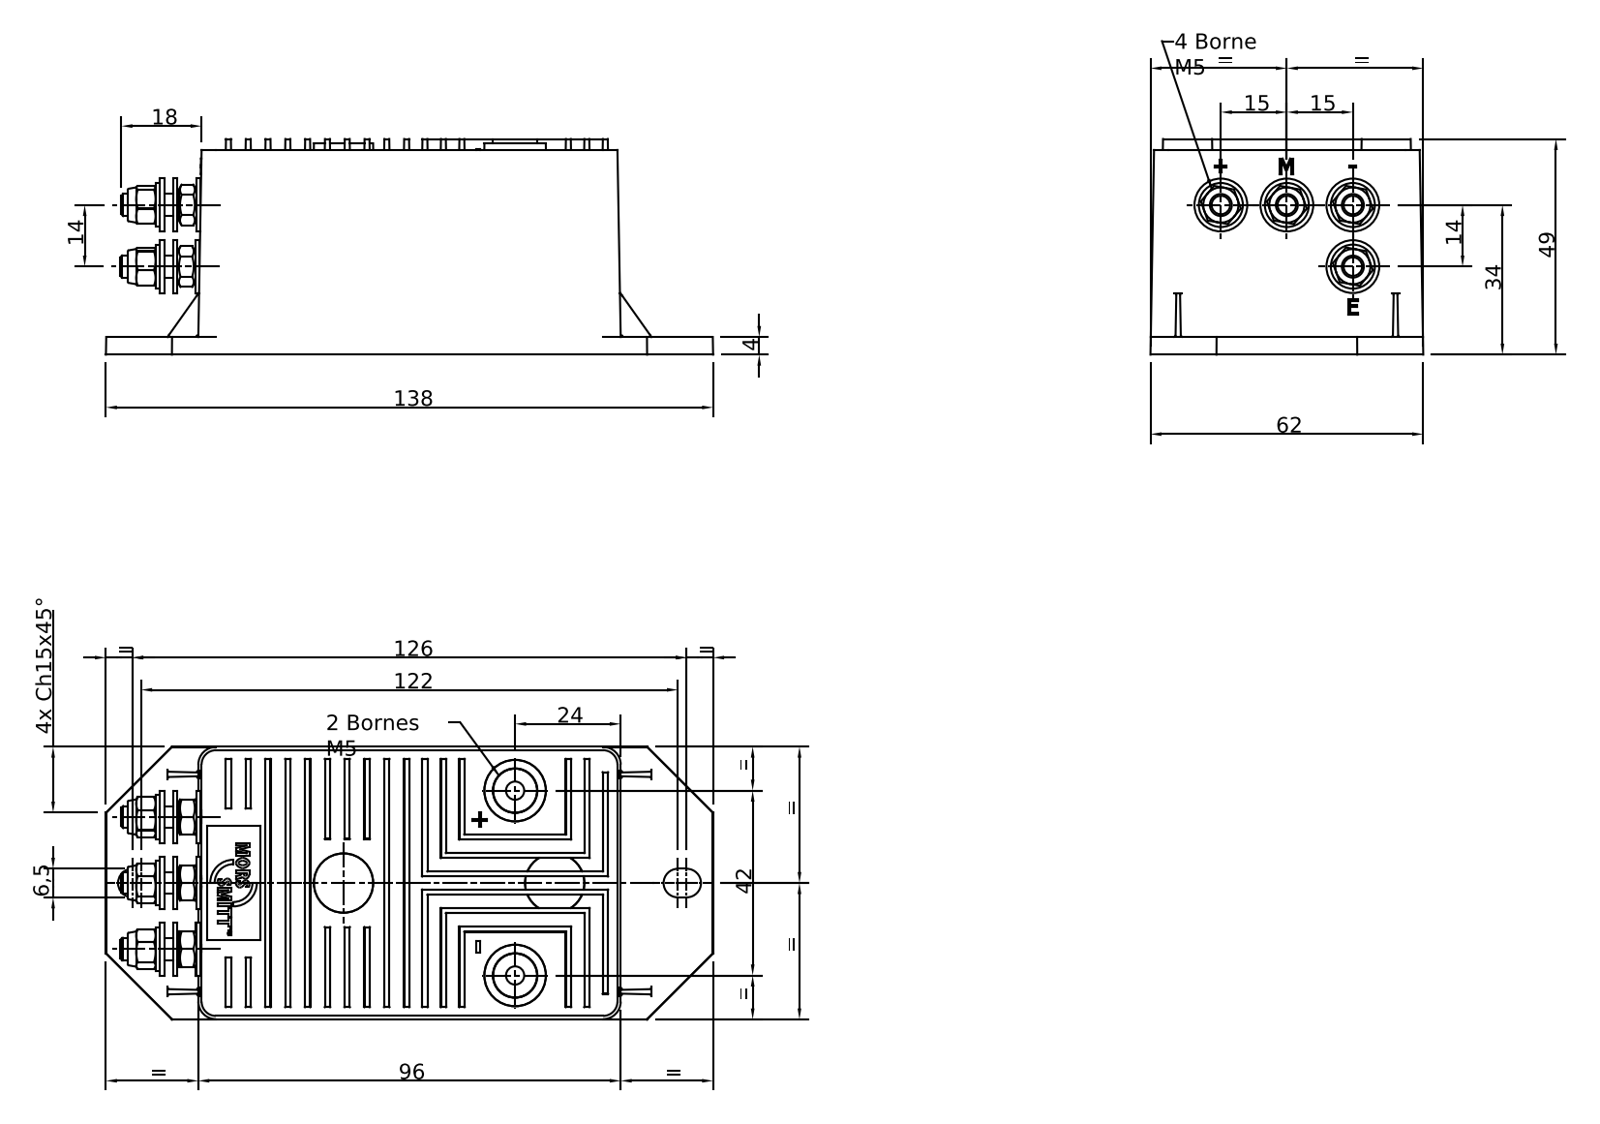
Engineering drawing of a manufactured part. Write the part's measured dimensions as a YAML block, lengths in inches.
part_name: "MSV100-1000-0199_Enveloppe_1"
step_written_by: "Autodesk Inventor 2012 (AUTOMOTIVE_DESIGN)"
units: inches
bodies: {solids: 0, faces: 424, planar: 302, cylindrical: 56, other: 66}
overall_size: [5.433, 2.441, 1.93]
round_holes:
  - {diameter: 0.163, count: 2}
round_bosses_or_shafts:
  - {diameter: 0.394, count: 6}
  - {diameter: 0.472, count: 4}
  - {diameter: 0.197, count: 4}
partial_cylinders:
  - {radius: 0.079, count: 16}
  - {radius: 0.02, count: 12}
face_to_face_distances: [0.079, 1.831, 0.157, 1.673, 0.177, 0.354, 1.752, 0.165, 0.039, 0.531]
hole_center_spacings: [1.654]
